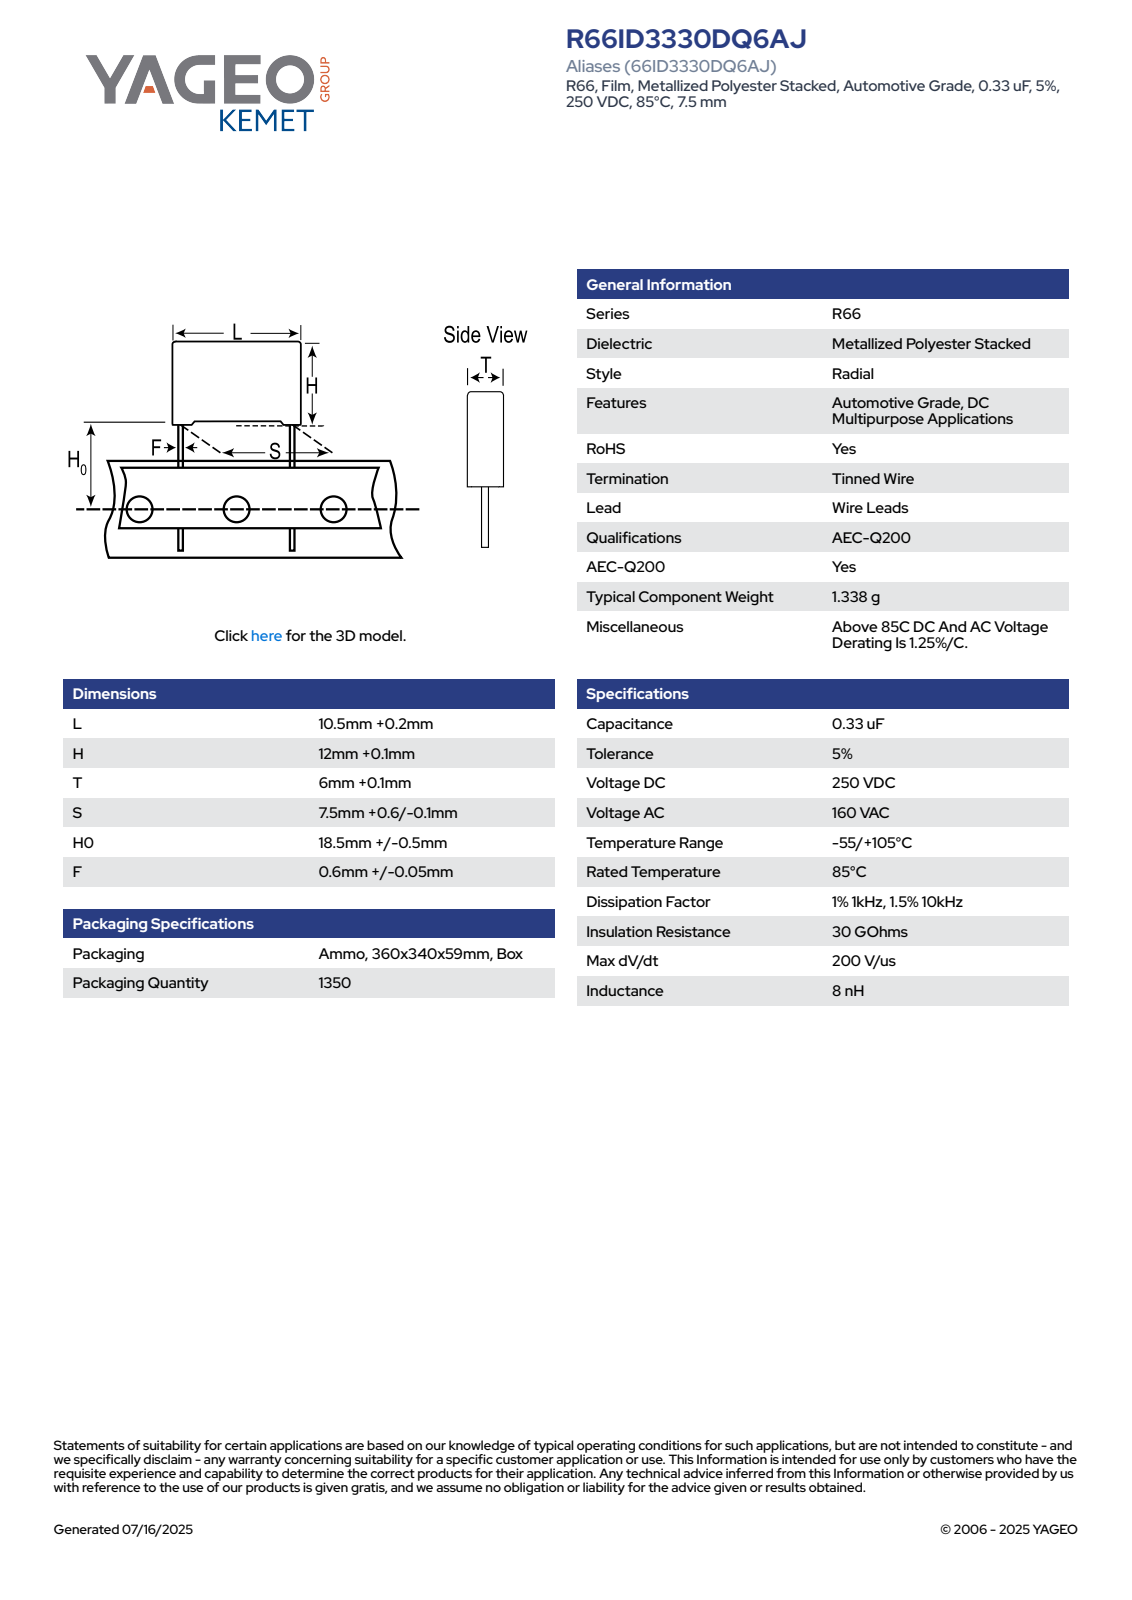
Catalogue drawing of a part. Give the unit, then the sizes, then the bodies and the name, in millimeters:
Units: millimetres
Overall size (bounding box): 31.1 × 10.7 × 6.11
Round bosses / shafts (diameter × count): ⌀0.65 ×2
Partial cylindrical surfaces — rounded edges, fillets, slot ends (radius × count): R0.5 ×4
Main face-to-face distances: 6.1, 10.7, 11.35, 0.36, 5.74, 0.75, 12.1, 10.34, 5.38, 9.98
Volume: 760 mm³ · Surface area: 635 mm²
Bodies: 4 solids, 85 faces (77 planar, 8 cylindrical, 0 other)
Part name (STEP PRODUCT): CFR_RB2_10.5X12X6_L10.7H12.1T6.1S7.5H019F0.65
STEP written by: SolidWorks 2020 (AUTOMOTIVE_DESIGN)
